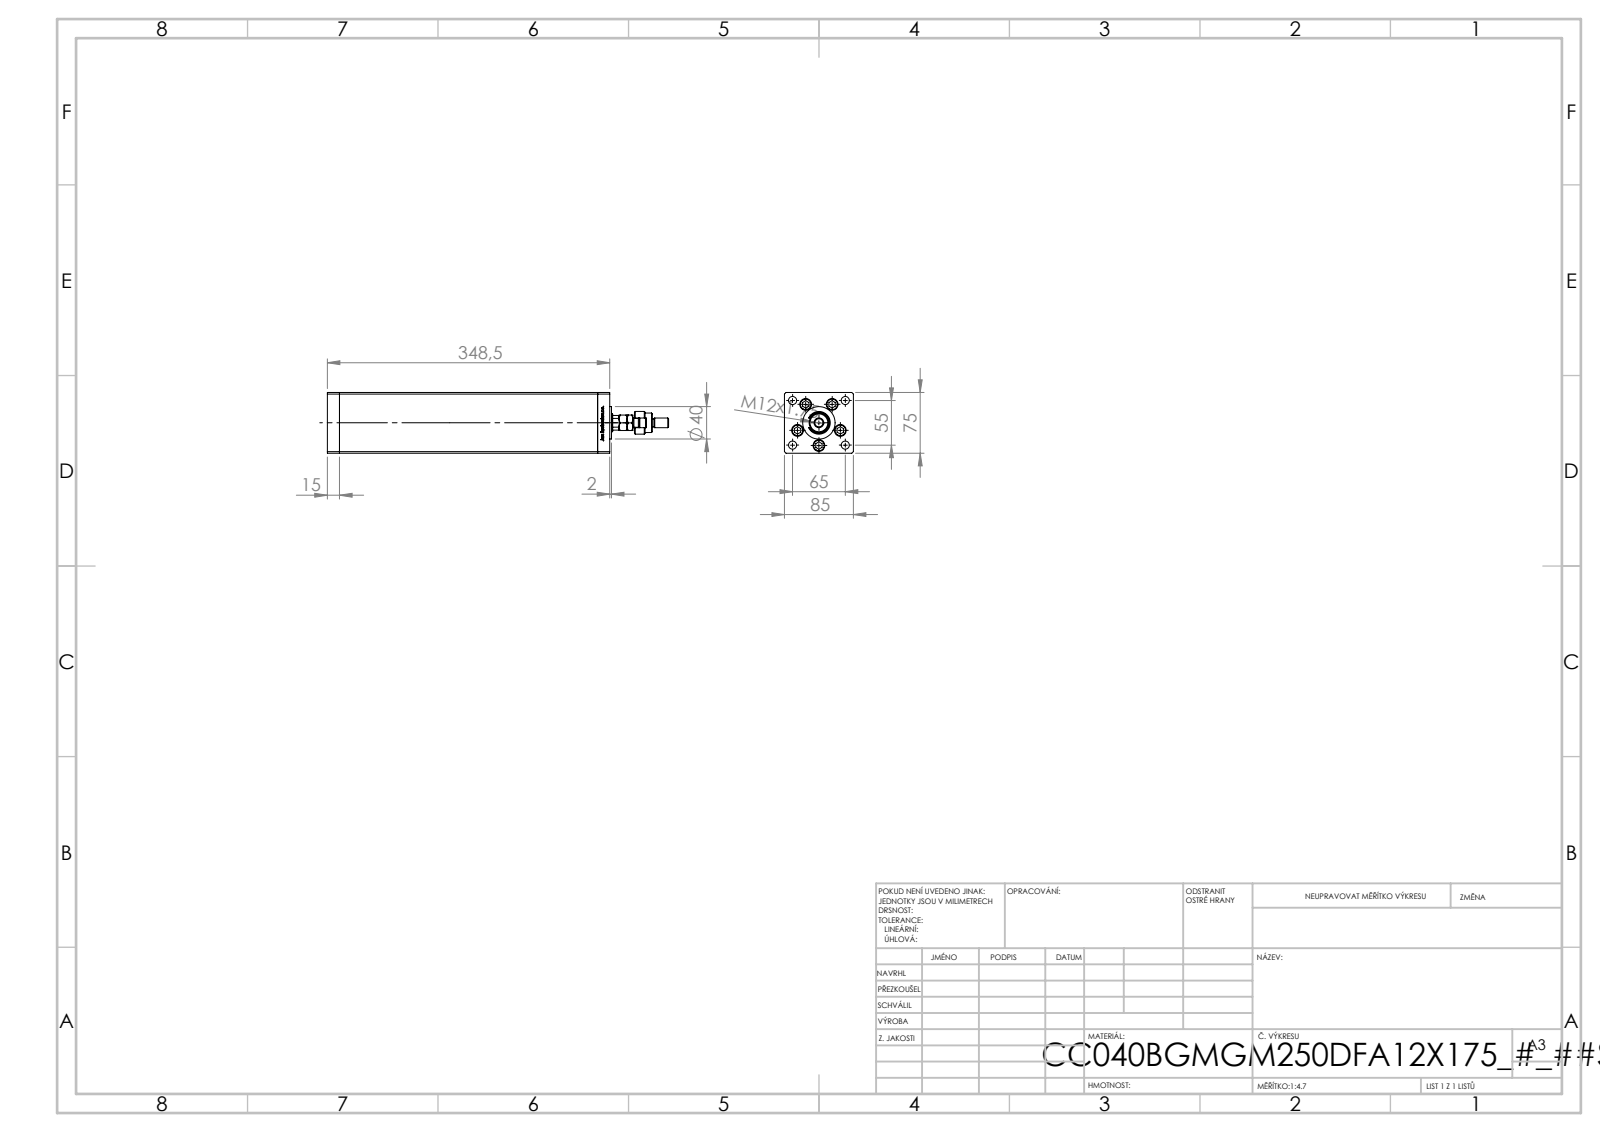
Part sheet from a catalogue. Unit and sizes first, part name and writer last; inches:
Units: inches
Overall size (bounding box): 16.575 × 3.346 × 2.953
Round holes (diameter × count): ⌀0.433 ×5, ⌀0.571 ×5, ⌀0.394 ×4, ⌀0.079 ×2, ⌀0.518 ×2, ⌀0.531 ×1, ⌀0.866 ×1
Round bosses / shafts (diameter × count): ⌀0.315 ×5, ⌀1.575 ×1, ⌀1.102 ×1, ⌀0.945 ×1, ⌀0.709 ×1, ⌀0.472 ×1, ⌀0.433 ×1, ⌀0.394 ×1
Partial cylindrical surfaces — rounded edges, fillets, slot ends (radius × count): R0.037 ×2, R0.384 ×1, R0.413 ×1
Main face-to-face distances: 3.346, 2.953, 0.591, 12.539, 13.13, 2.539, 0.413, 1.23, 2.116, 2.697
Hole centre spacings: 1.102, 1.676, 0.664, 0.755, 1.273, 1.28, 1.324, 1.47
Volume: 117.8 in³ · Surface area: 400.6 in²
Bodies: 16 solids, 1268 faces (490 planar, 160 cylindrical, 618 other)
Part name (STEP PRODUCT): MFA; ALLEN BOLT; FEMALE_PART_FOR_DFA; V220C_B MIDDLE (+3 more)
STEP written by: SolidWorks 2019 (CONFIG_CONTROL_DESIGN)
